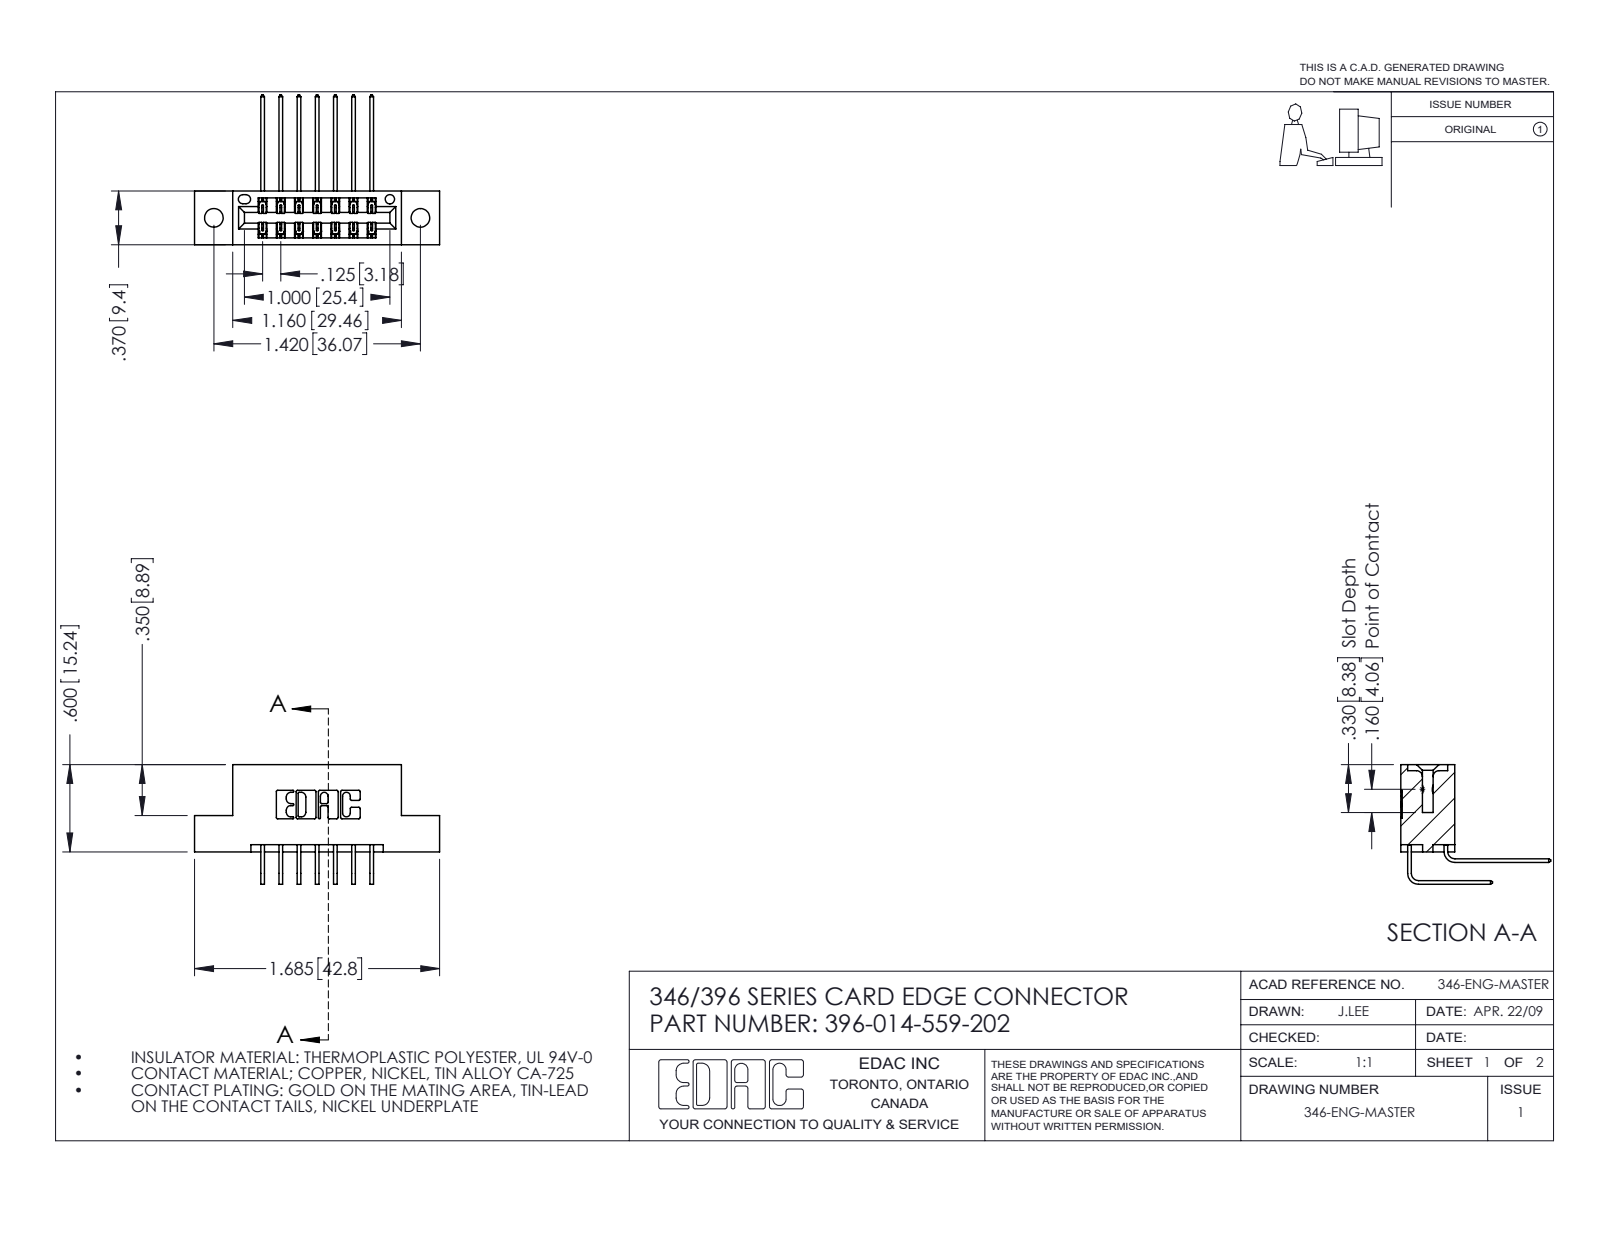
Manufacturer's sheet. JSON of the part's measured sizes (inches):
{"part_name": "346 Part_Flush Mounting Lugs - 0.128 Dia; 345-292-001_558 559 Tail - 1; 396-014-559-202; 345-292-001_559 Tail - 2", "step_written_by": "SolidWorks 2016 (CONFIG_CONTROL_DESIGN)", "units": "inches", "bodies": {"solids": 15, "faces": 878, "planar": 594, "cylindrical": 284, "other": 0}, "overall_size": [1.685, 1.03, 0.823], "volume_in3": 0.241, "surface_area_in2": 7.737, "round_holes": [[0.128, 2], [0.064, 1]], "partial_cylinders_radius": [[0.01, 22], [0.006, 21], [0.007, 6], [0.031, 6], [0.026, 3], [0.014, 2], [0.022, 2], [0.024, 2]], "face_to_face_distances": [0.25, 0.048, 0.322, 0.37, 0.025, 0.298, 0.072, 0.125, 0.125, 0.148], "hole_center_spacings": [0.246, 1.217, 1.42]}
